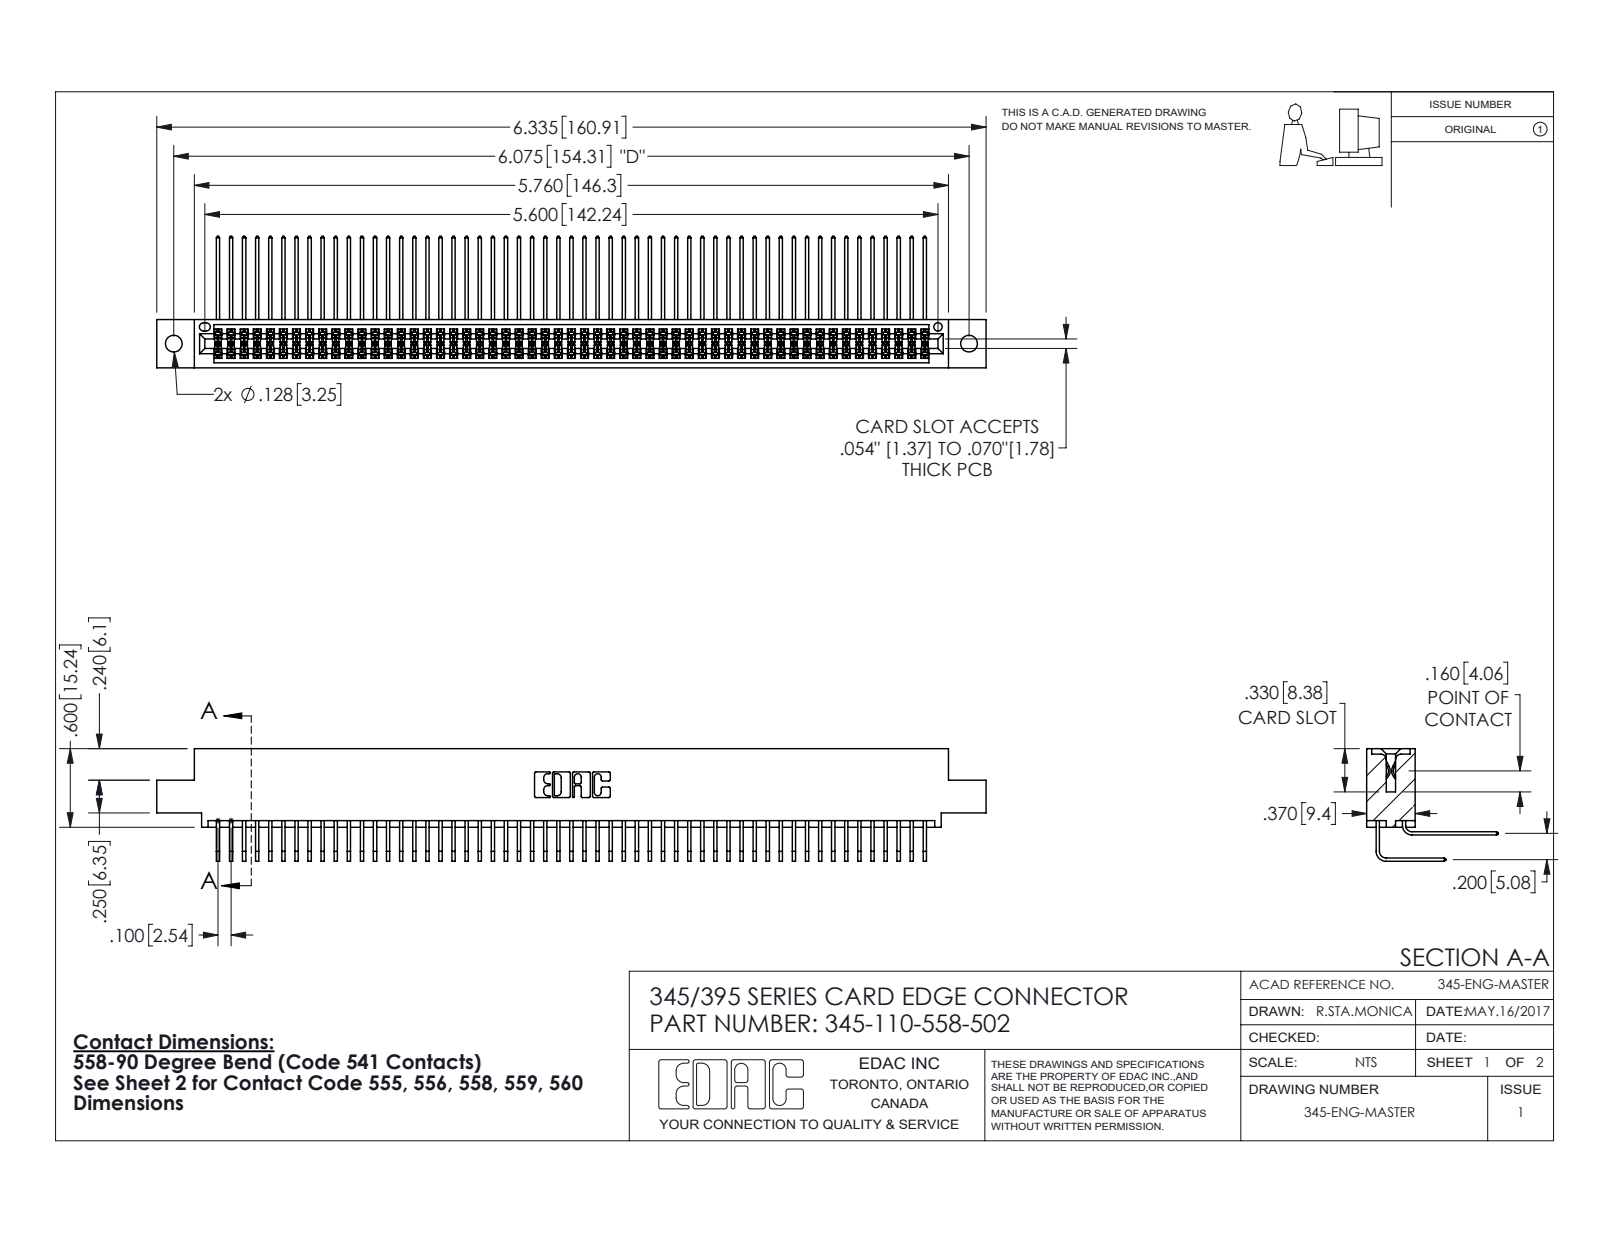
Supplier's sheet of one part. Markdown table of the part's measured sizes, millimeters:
| quantity | value |
| --- | --- |
| part name | 345-110-558-502; 345-292-001_558 559 Tail - 1; 345-292-001_558 Tail - 2; 345 Part_0.110 Offset - 0.128 Dia |
| STEP written by | SolidWorks 2016 (CONFIG_CONTROL_DESIGN) |
| units | millimeters |
| bodies | 111 solids, 5850 faces (3934 planar, 1916 cylindrical, 0 other) |
| overall size | 160.9 × 25.5 × 21.8 |
| volume | 16 300 mm³ |
| surface area | 27 120 mm² |
| round holes (diameter × count) | 3.3 × 2, 1.6 × 1 |
| partial cylindrical surfaces (radius × count) | 0.2 × 220, 0.3 × 22, 0.2 × 6, 0.8 × 6, 0.7 × 3, 0.4 × 2, 0.5 × 2, 0.6 × 2 |
| main face-to-face distances | 1.8, 7.6, 5.1, 9.4, 2.5, 6.9, 0.6, 5.7, 0.6, 4.4 |
| hole center spacings | 6.9, 148.3, 154.3 |
